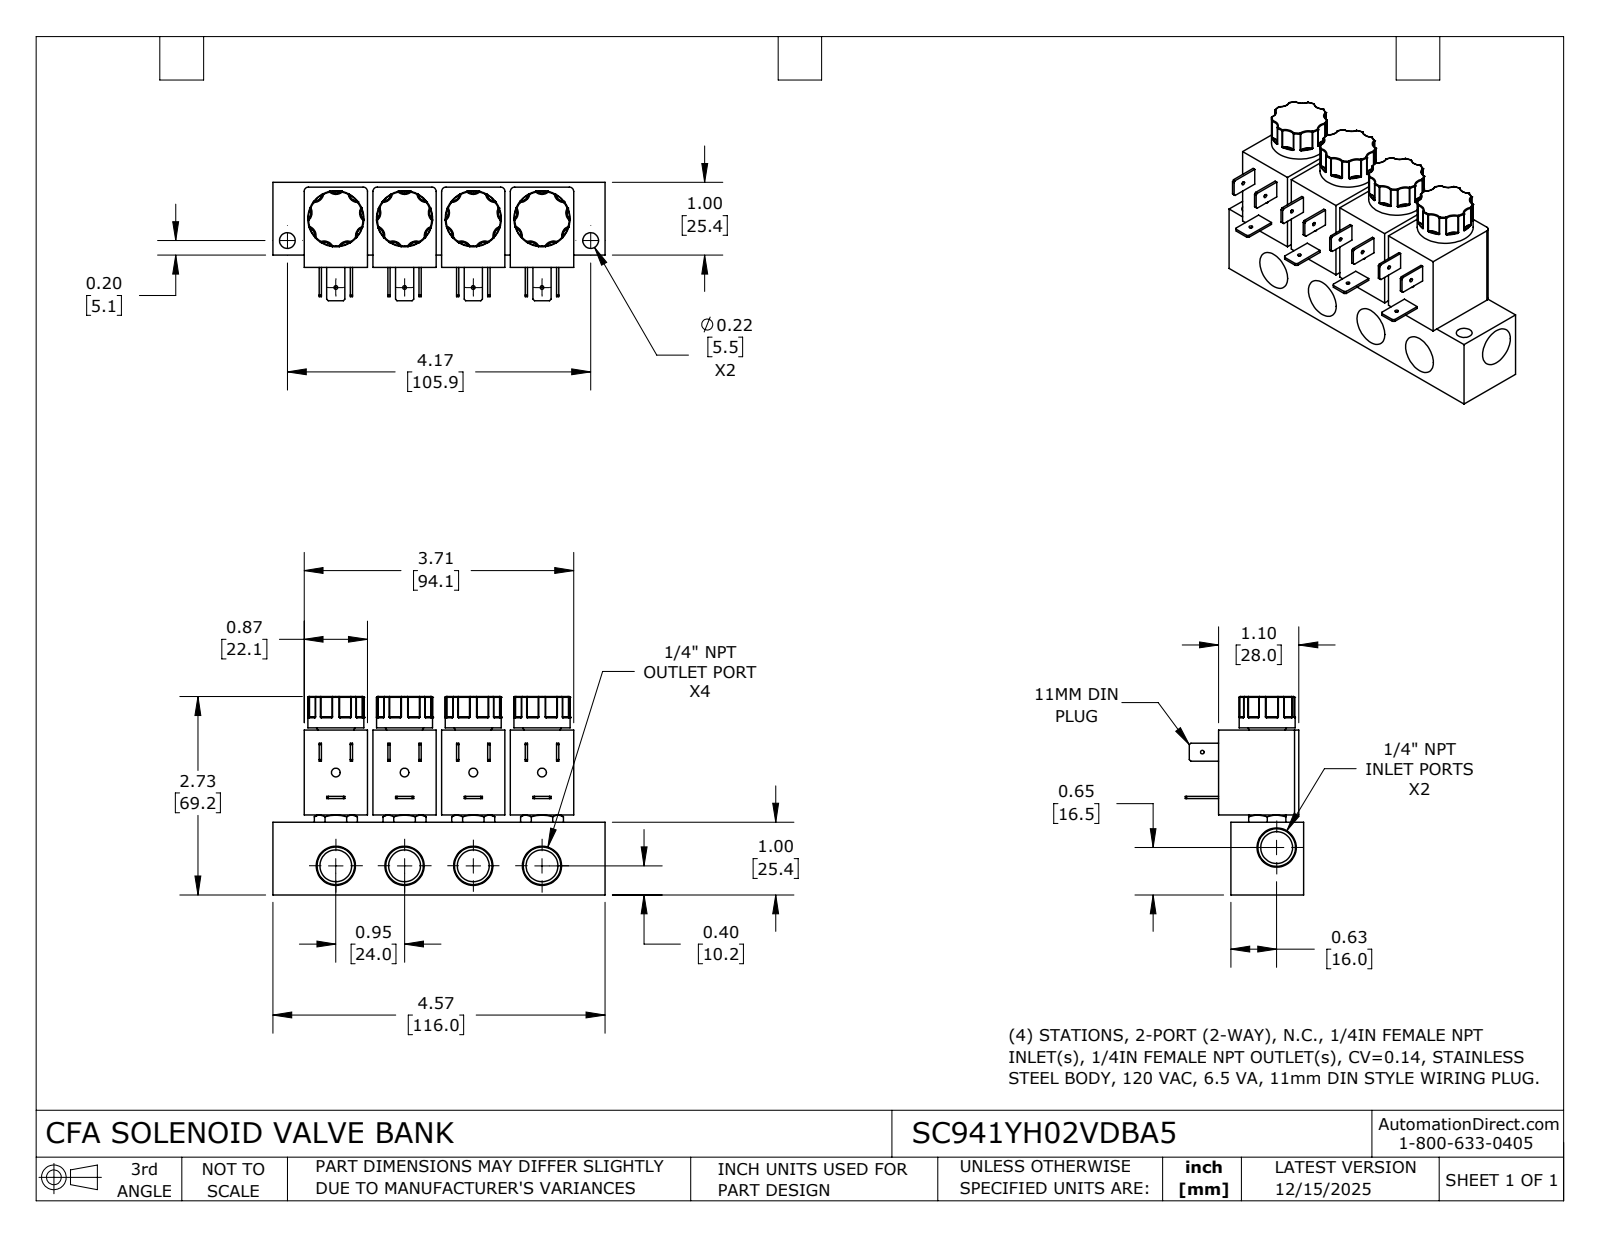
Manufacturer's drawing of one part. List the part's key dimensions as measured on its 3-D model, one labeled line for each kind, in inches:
Part name (STEP PRODUCT): SC941YH02VDBA5
STEP written by: SolidWorks 2024 (CONFIG_CONTROL_DESIGN)
Units: inches
Bodies: 1 solid, 868 faces (192 planar, 184 cylindrical, 492 other)
Overall size (bounding box): 4.567 × 2.725 × 1.627
Volume: 9.182 in³ · Surface area: 61.05 in²
Round holes (diameter × count): ⌀0.05 ×5, ⌀0.438 ×5, ⌀0.12 ×4, ⌀0.217 ×2
Round bosses / shafts (diameter × count): ⌀0.77 ×4
Partial cylindrical surfaces — rounded edges, fillets, slot ends (radius × count): R0.01 ×72, R0.133 ×34, R0.06 ×8, R0.132 ×2
Main face-to-face distances: 1, 0.945, 1.169, 1.89, 1.815, 0.87, 0.169, 0.065, 0.935, 1.104
Hole centre spacings: 0.945, 1.282, 1.593, 0.945, 1.89, 1.89, 2.835, 1.593
